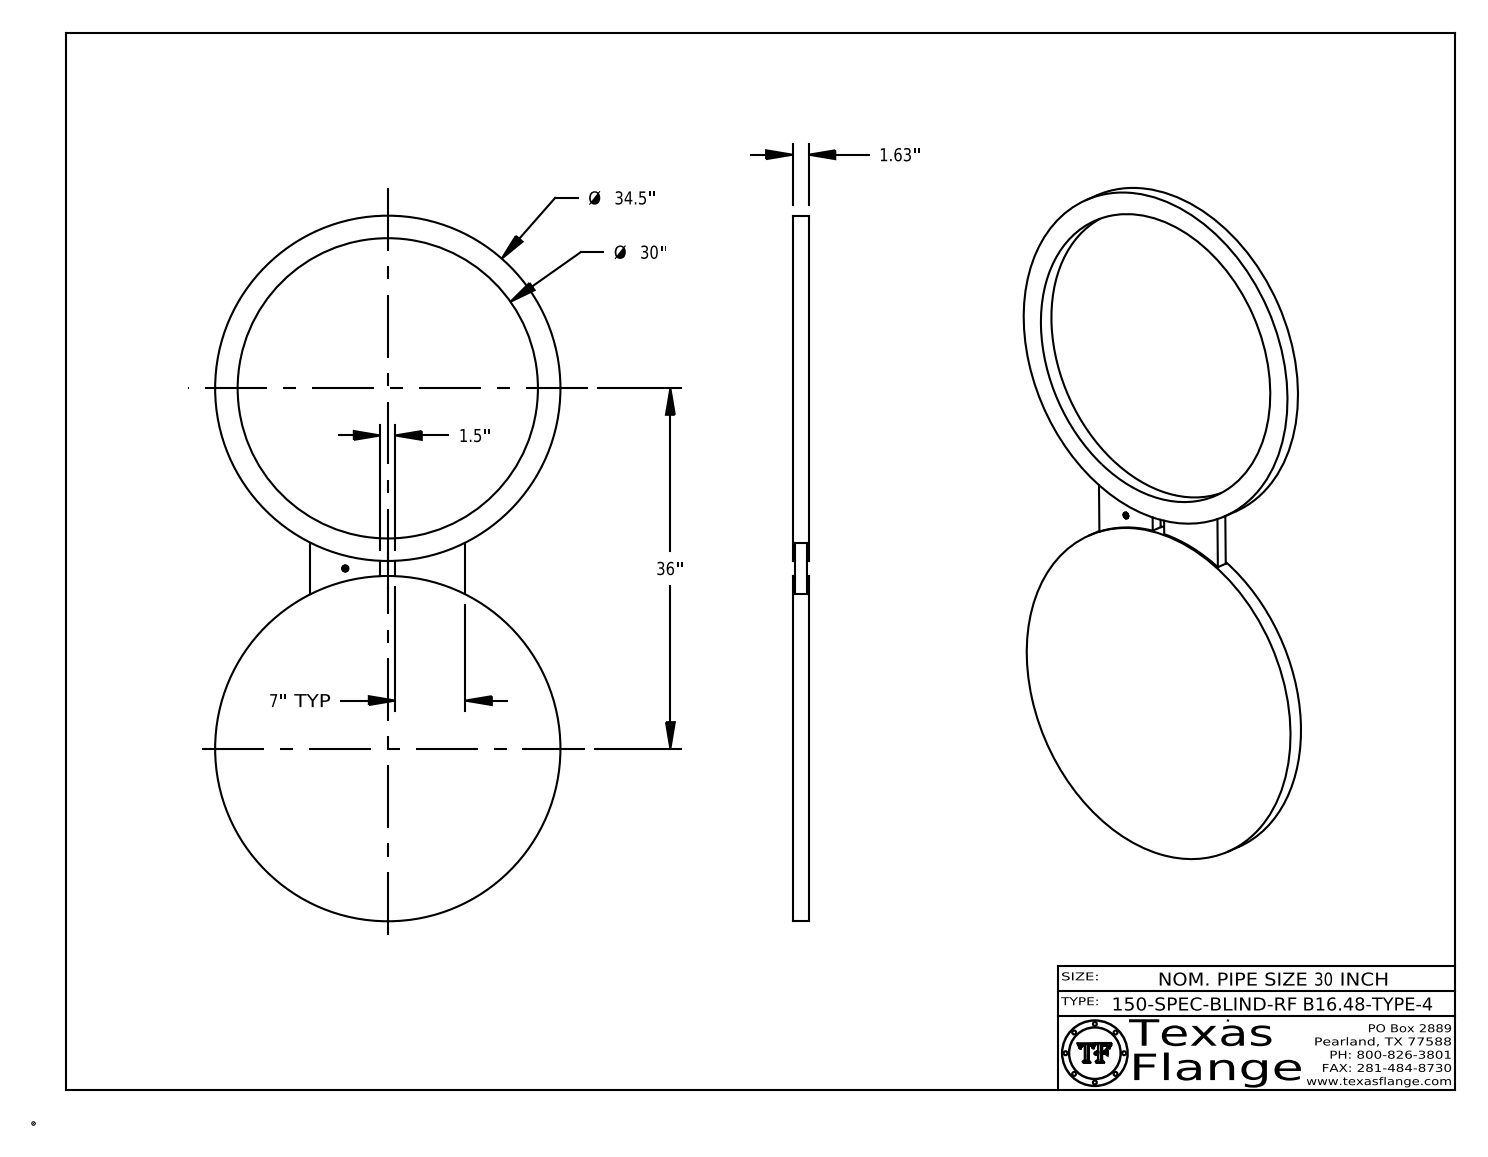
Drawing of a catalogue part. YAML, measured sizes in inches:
part_name: "30-150-SPEC-BLIND-RF-B16.48-TYPE-4"
step_written_by: "CATIA V5 STEP AP214 (AUTOMOTIVE_DESIGN)"
units: inches
bodies: {solids: 1, faces: 403, planar: 377, cylindrical: 26, other: 0}
overall_size: [70.5, 34.5, 1.625]
volume: 1938
surface_area: 2891
round_holes:
  - {diameter: 0.625, count: 1}
  - {diameter: 30, count: 1}
round_bosses_or_shafts:
  - {diameter: 0.038, count: 8}
  - {diameter: 34.5, count: 2}
  - {diameter: 0.492, count: 1}
face_to_face_distances: [1.625, 0.203, 1.422, 1.219, 15.5, 7, 8.5, 1.5, 1.407, 1.204]
hole_center_spacings: [18.495]
